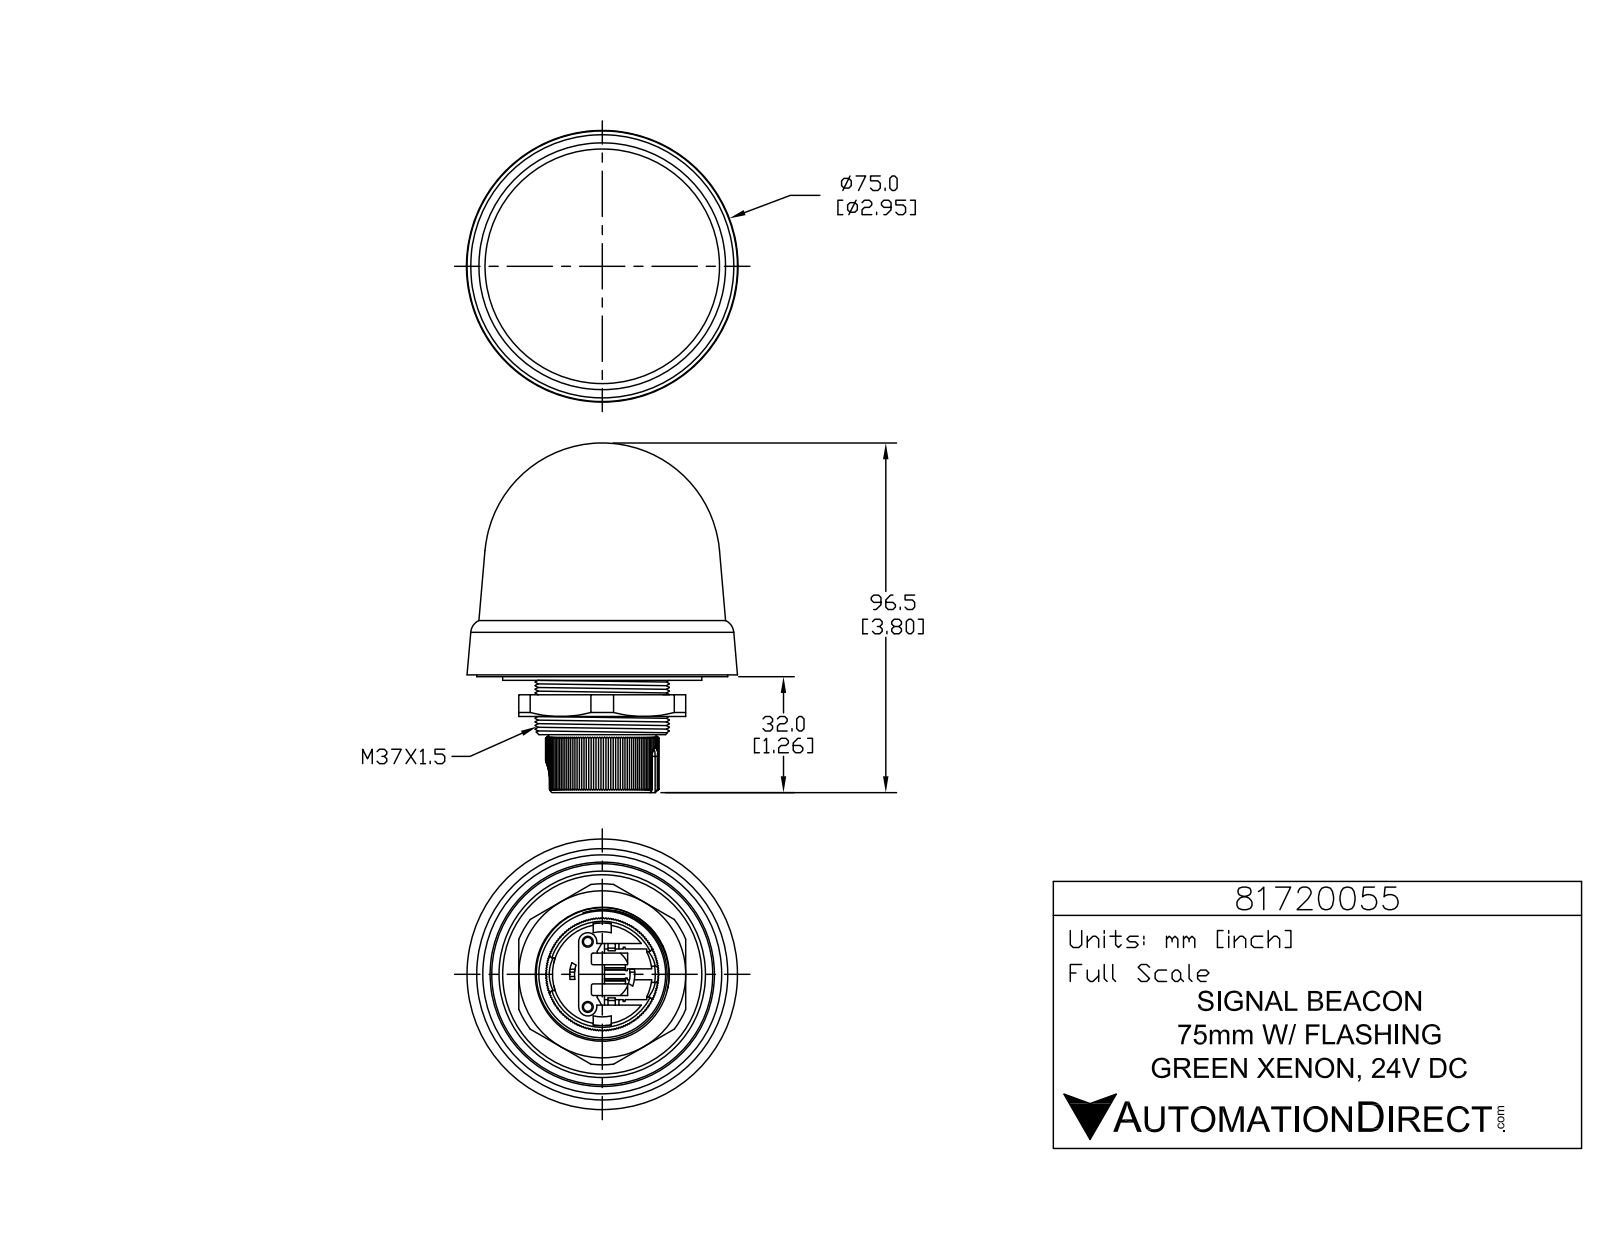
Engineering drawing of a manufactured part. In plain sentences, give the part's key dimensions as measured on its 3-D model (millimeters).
The part is named "81720055". Its 3-D file was written by "SolidWorks 2019 (CONFIG_CONTROL_DESIGN)". It is 3 solids with 560 faces: 432 planar, 80 cylindrical and 48 other. Overall it measures 96.5 by 74.7 by 74.7 millimeters. Its volume is 202 500 cubic millimeters and its surface area 37 860 square millimeters. Round holes: 2 of diameter 2.4, 2 of diameter 3, 1 of diameter 15.3, 1 of diameter 29. Round bosses or shafts: 2 of diameter 5.5, 2 of diameter 1.7, 1 of diameter 55, 1 of diameter 37, 1 of diameter 23.5. Partial cylindrical surfaces (rounded edges, fillets, slot ends): 6 of radius 0.2, 6 of radius 1, 4 of radius 0.5, 2 of radius 0.8, 2 of radius 2, 2 of radius 2.5, 1 of radius 4.5, 1 of radius 9. The main face-to-face distances are 4.5, 9, 5, 11, 13, 8.5, 1.5, 10, 3, 4. The hole center spacings are 9.9, 18.
